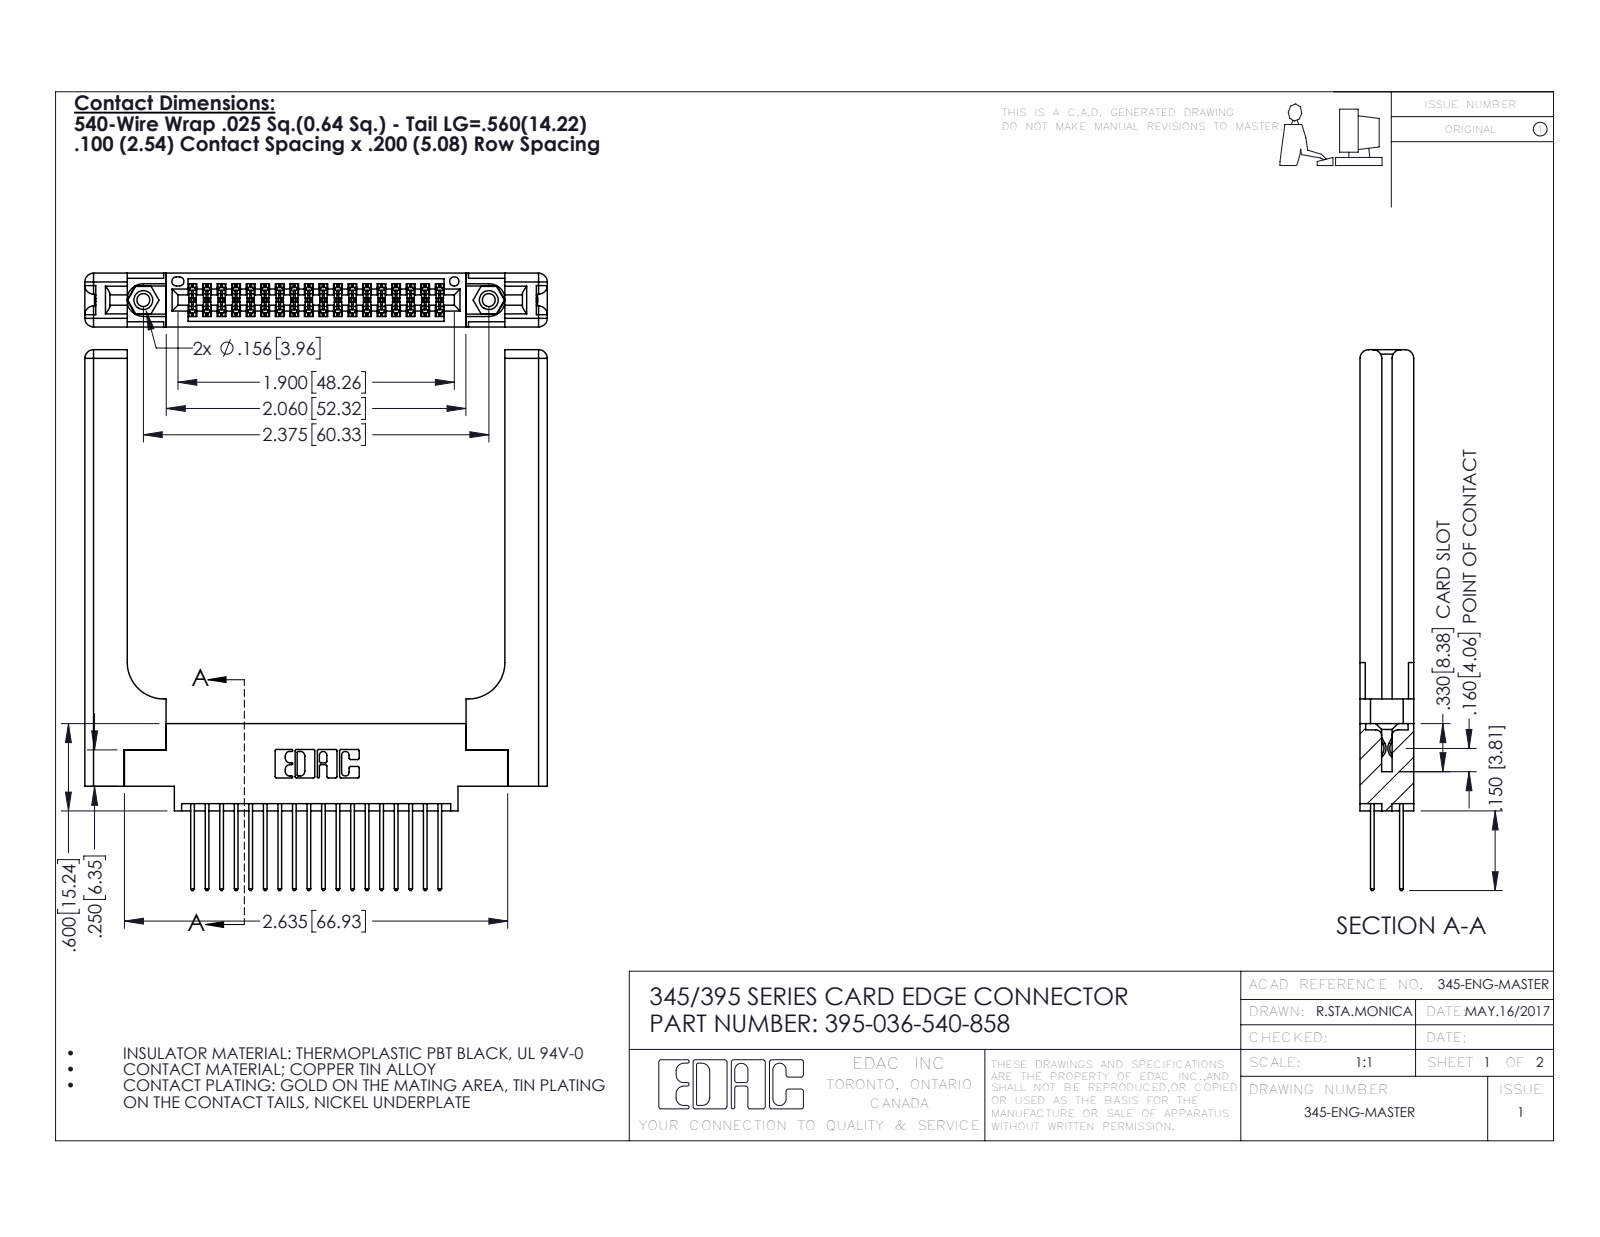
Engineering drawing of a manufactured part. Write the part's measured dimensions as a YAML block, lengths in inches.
part_name: "395-036-540-858; 345-292-001_345-293-140; 345 Part_0.170 Offset - 0.156 Dia-TH; 345-250-001_345-250-001-102 (+1 more)"
step_written_by: "SolidWorks 2016 (CONFIG_CONTROL_DESIGN)"
units: inches
bodies: {solids: 41, faces: 2186, planar: 1420, cylindrical: 706, other: 60}
overall_size: [3.717, 3.179, 0.37]
volume: 0.984
surface_area: 25.84
round_holes:
  - {diameter: 0.089, count: 2}
  - {diameter: 0.125, count: 2}
  - {diameter: 0.156, count: 2}
  - {diameter: 0.064, count: 1}
round_bosses_or_shafts:
  - {diameter: 0.155, count: 2}
partial_cylinders:
  - {radius: 0.006, count: 54}
  - {radius: 0.01, count: 36}
  - {radius: 0.01, count: 22}
  - {radius: 0.06, count: 16}
  - {radius: 0.007, count: 6}
  - {radius: 0.031, count: 6}
  - {radius: 0.026, count: 3}
  - {radius: 0.014, count: 2}
face_to_face_distances: [0.37, 0.072, 0.298, 0.098, 0.272, 0.025, 0.2, 0.148, 0.15, 0.225]
hole_center_spacings: [0.27, 2.141, 2.375]
